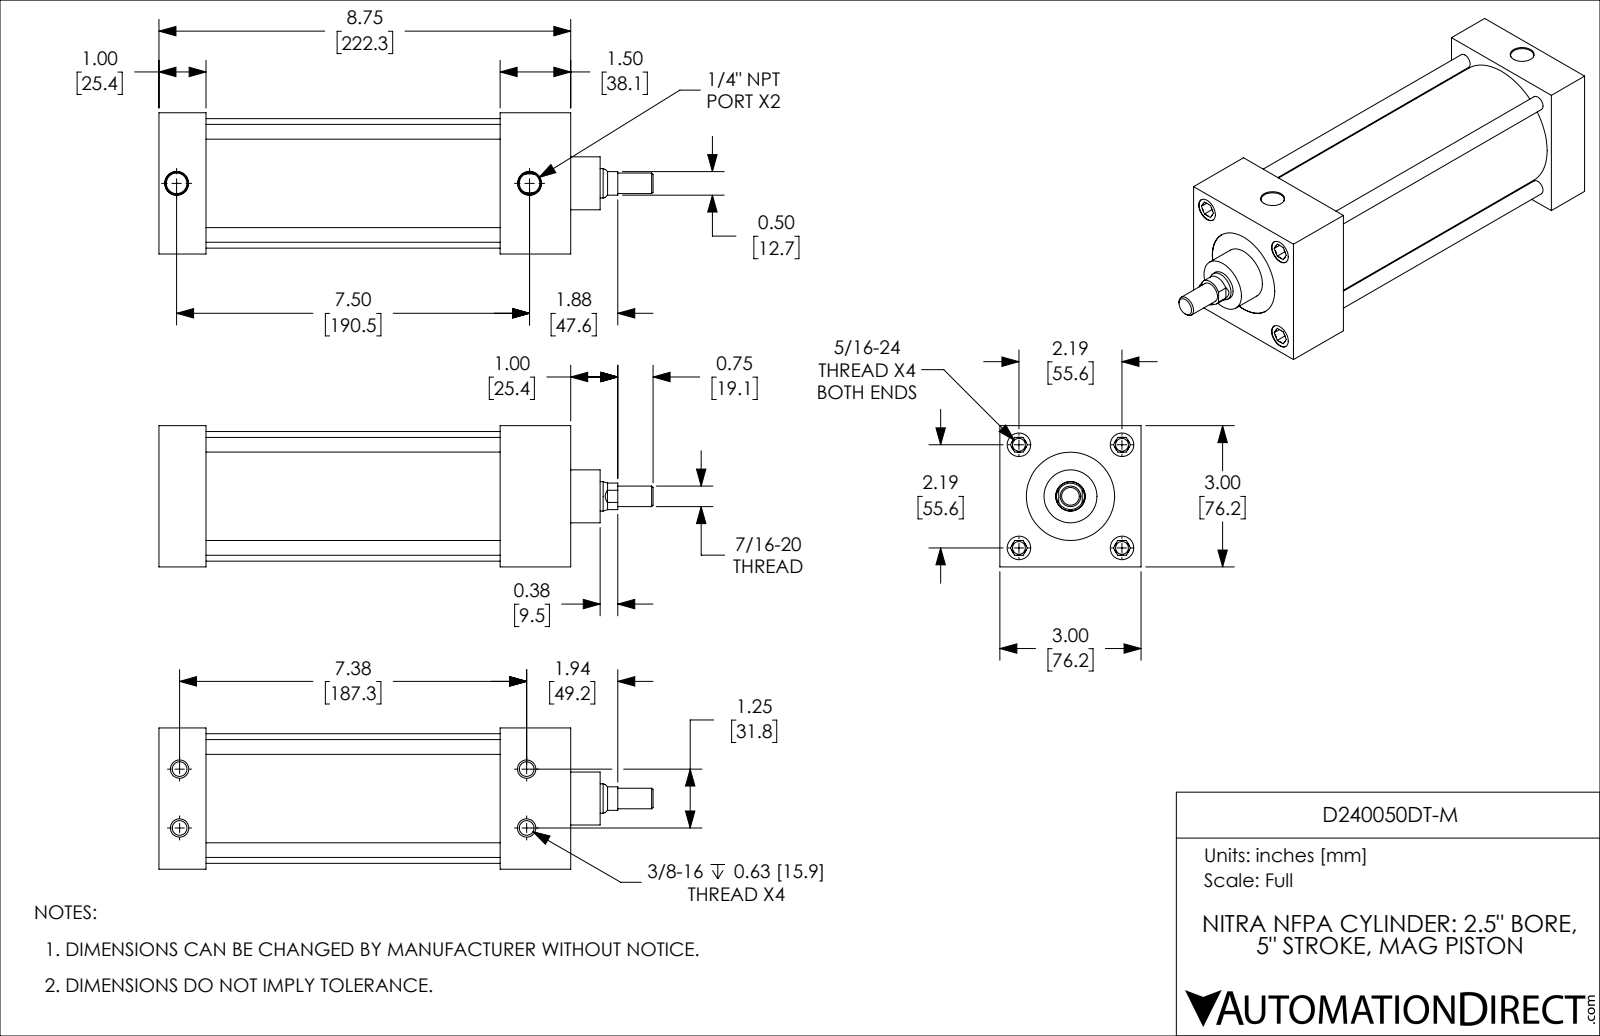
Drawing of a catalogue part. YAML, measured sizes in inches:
part_name: "D240050DT-M; D240050DT-M_PISTON_KK1; D240050DT-M_BODY"
step_written_by: "SolidWorks 2019 (CONFIG_CONTROL_DESIGN)"
units: inches
bodies: {solids: 2, faces: 200, planar: 58, cylindrical: 62, other: 80}
overall_size: [10.5, 3, 3]
volume: 38.25
surface_area: 244
round_holes:
  - {diameter: 0.272, count: 4}
  - {diameter: 0.313, count: 4}
  - {diameter: 0.5, count: 4}
  - {diameter: 0.438, count: 2}
  - {diameter: 0.626, count: 1}
  - {diameter: 1.875, count: 1}
  - {diameter: 2.501, count: 1}
round_bosses_or_shafts:
  - {diameter: 0.312, count: 4}
  - {diameter: 2.751, count: 1}
  - {diameter: 2.499, count: 1}
  - {diameter: 1.125, count: 1}
  - {diameter: 0.624, count: 1}
  - {diameter: 0.437, count: 1}
partial_cylinders:
  - {radius: 0.281, count: 1}
face_to_face_distances: [3, 1, 7.25, 6.25, 8.75, 7.75, 1.5, 1.25, 2.25, 5]
hole_center_spacings: [1.548, 2.19, 0.628, 0.628, 1.25, 3.097, 7.375, 7.464]
